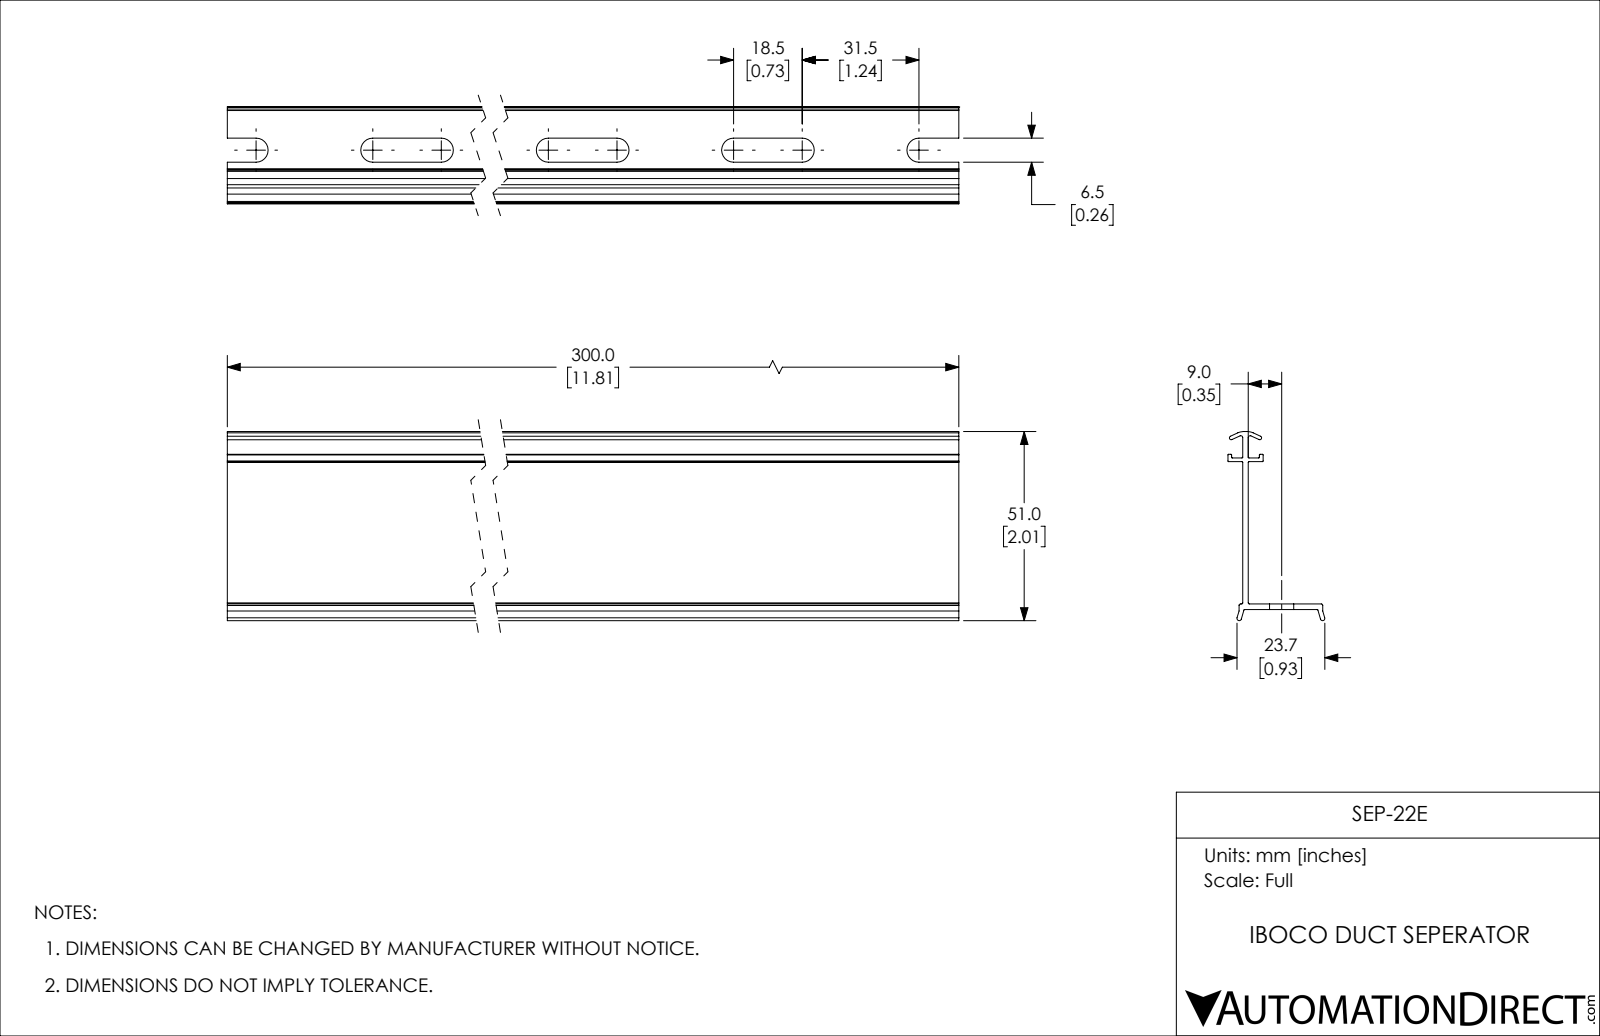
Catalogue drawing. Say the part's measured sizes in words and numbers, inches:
The part is named "SEP-22E". Its 3-D file was written by "SolidWorks 2019 (CONFIG_CONTROL_DESIGN)". It is 1 solid with 92 faces: 46 planar, 46 cylindrical and 0 other. Overall it measures 11.811 by 2.008 by 1.03 inches. Its volume is 2.267 cubic inches and its surface area 84.01 square inches. Partial cylindrical surfaces (rounded edges, fillets, slot ends): 14 of radius 0.008, 12 of radius 0.128, 4 of radius 0.02, 2 of radius 0.012, 2 of radius 0.016, 2 of radius 0.024, 2 of radius 0.157. The main face-to-face distances are 0.059, 0.039, 1.57, 1.511, 1.609, 1.55, 0.217, 0.157, 0.118, 0.256.
